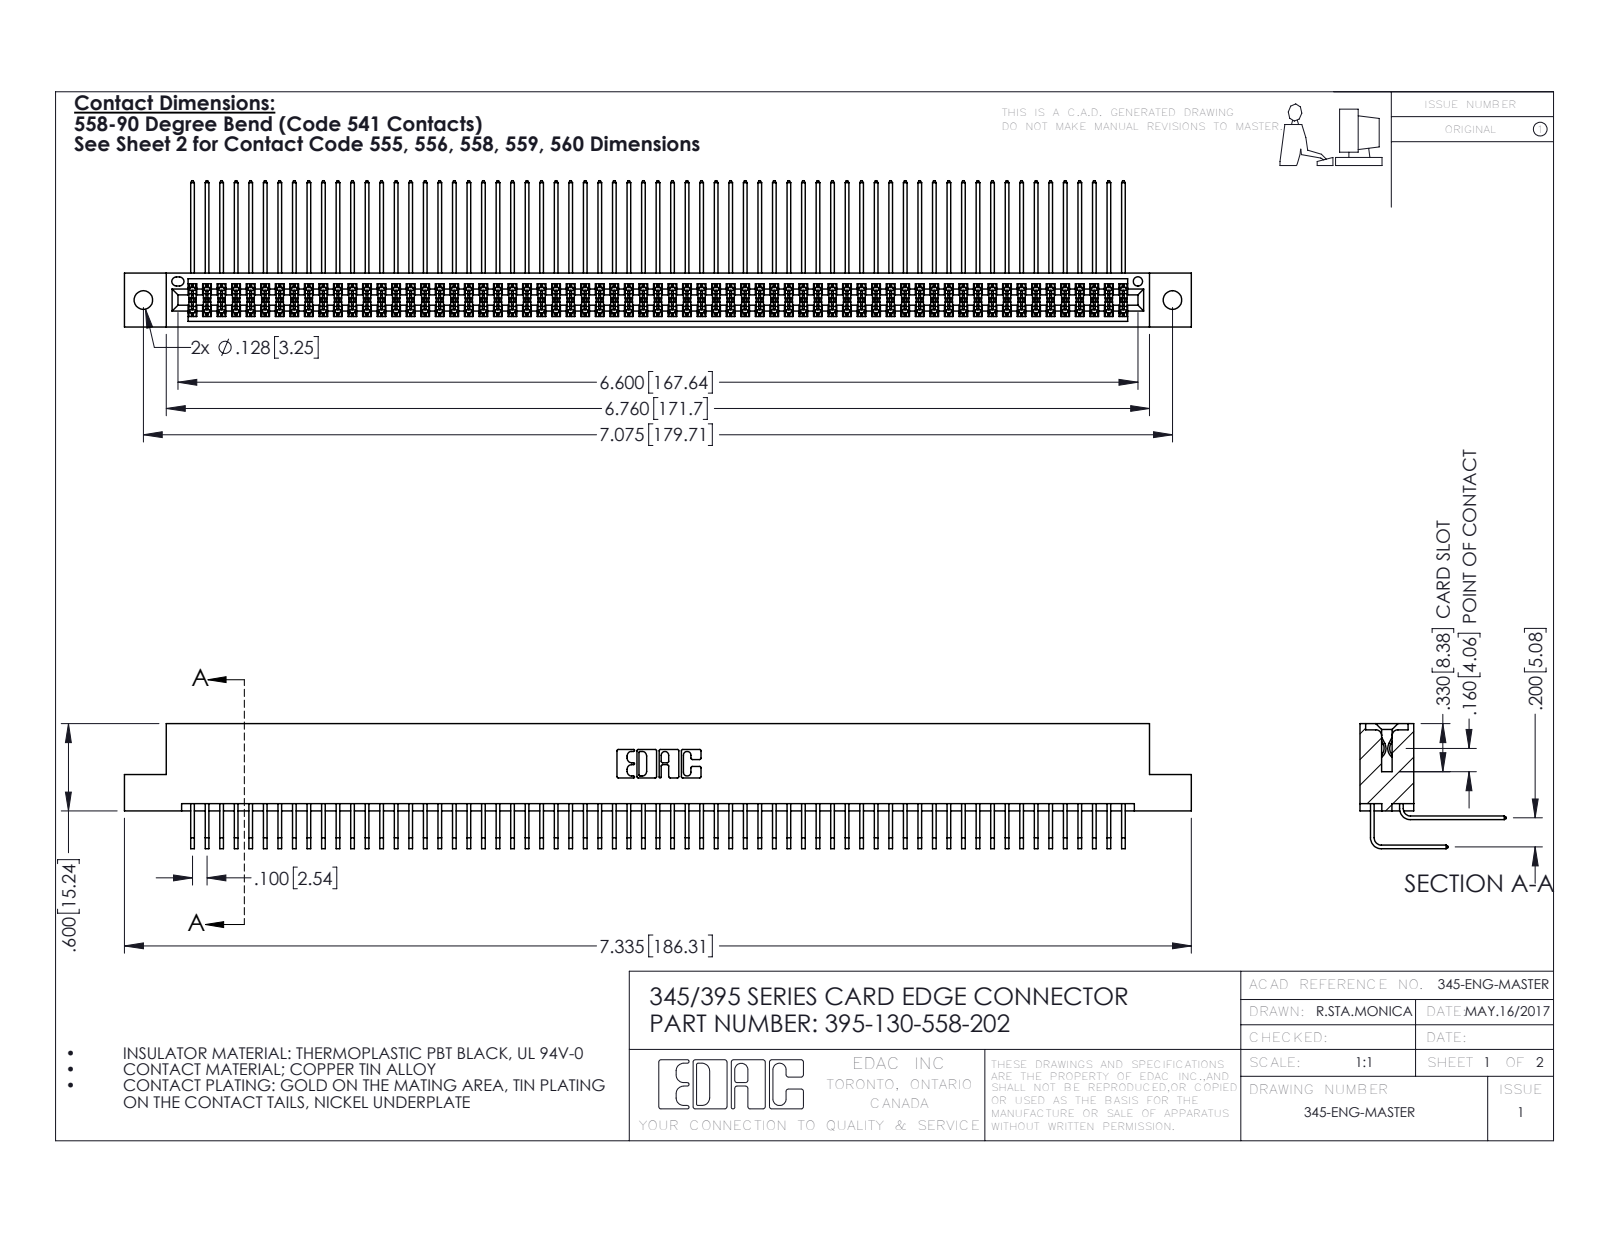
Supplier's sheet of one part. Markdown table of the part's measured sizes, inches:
| quantity | value |
| --- | --- |
| part name | 345 Part_Flush Mounting Lugs - 0.128 Dia; 395-130-558-202; 345-292-001_558 559 Tail - 1; 345-292-001_558 Tail - 2 |
| STEP written by | SolidWorks 2016 (CONFIG_CONTROL_DESIGN) |
| units | inches |
| bodies | 131 solids, 6886 faces (4630 planar, 2256 cylindrical, 0 other) |
| overall size | 7.335 × 1.005 × 0.859 |
| volume | 1.161 in³ |
| surface area | 49.32 in² |
| round holes (diameter × count) | 0.128 × 2, 0.064 × 1 |
| partial cylindrical surfaces (radius × count) | 0.006 × 195, 0.01 × 22, 0.007 × 6, 0.031 × 6, 0.026 × 3, 0.014 × 2, 0.019 × 2, 0.022 × 2 |
| main face-to-face distances | 0.072, 0.298, 0.2, 0.37, 0.098, 0.272, 0.025, 0.225, 0.025, 0.175 |
| hole center spacings | 0.27, 6.839, 7.075 |
